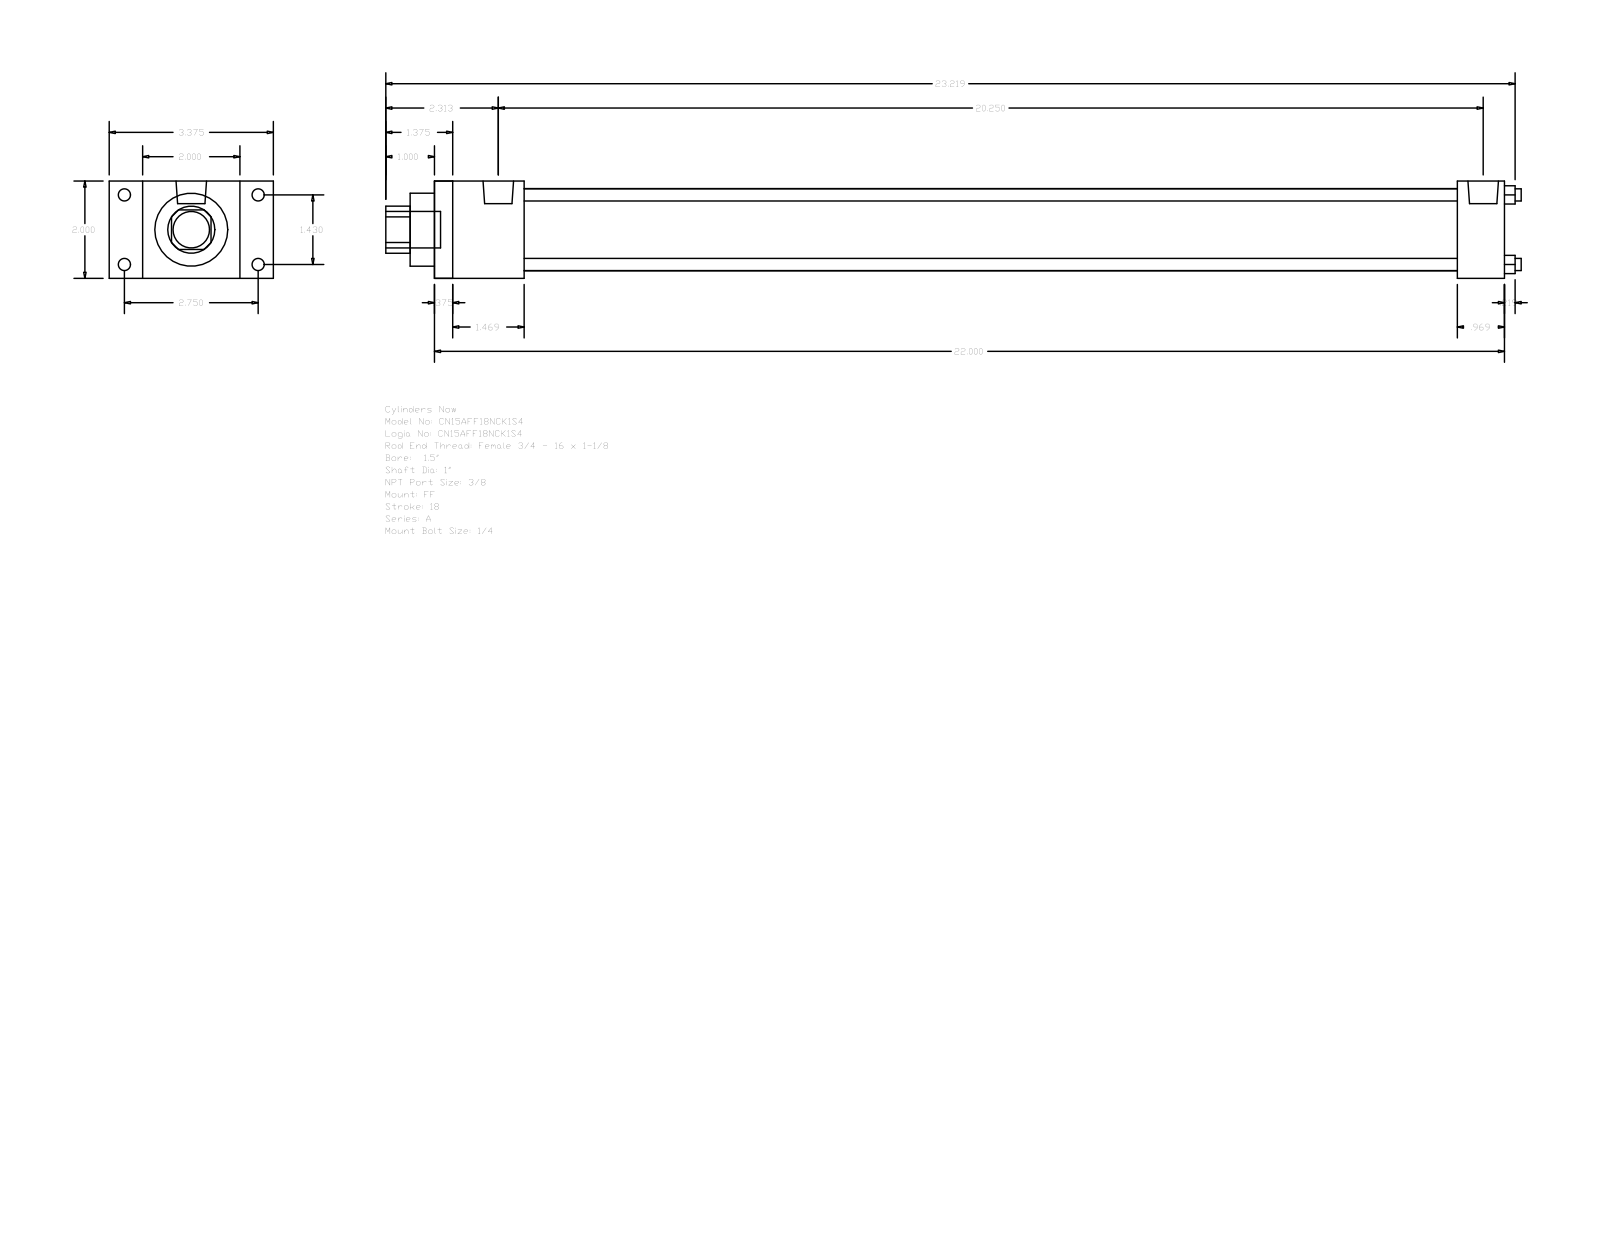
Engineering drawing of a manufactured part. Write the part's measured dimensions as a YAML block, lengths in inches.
part_name: "A_FF__0150_1"
step_written_by: "GSSL Pune (CONFIG_CONTROL_DESIGN)"
units: inches
bodies: {solids: 0, faces: 92, planar: 64, cylindrical: 28, other: 0}
overall_size: [23.344, 3.375, 2]
round_holes:
  - {diameter: 0.25, count: 4}
  - {diameter: 1, count: 1}
  - {diameter: 1.5, count: 1}
  - {diameter: 1.69, count: 1}
round_bosses_or_shafts:
  - {diameter: 0.25, count: 4}
  - {diameter: 0.219, count: 4}
  - {diameter: 0.627, count: 2}
  - {diameter: 0.75, count: 1}
partial_cylinders:
  - {radius: 0.484, count: 1}
face_to_face_distances: [2, 22, 0.375, 21.625, 1.844, 21.031, 1.469, 20.656, 19.187, 20.156]
hole_center_spacings: [1.011, 1.43, 2.022]
